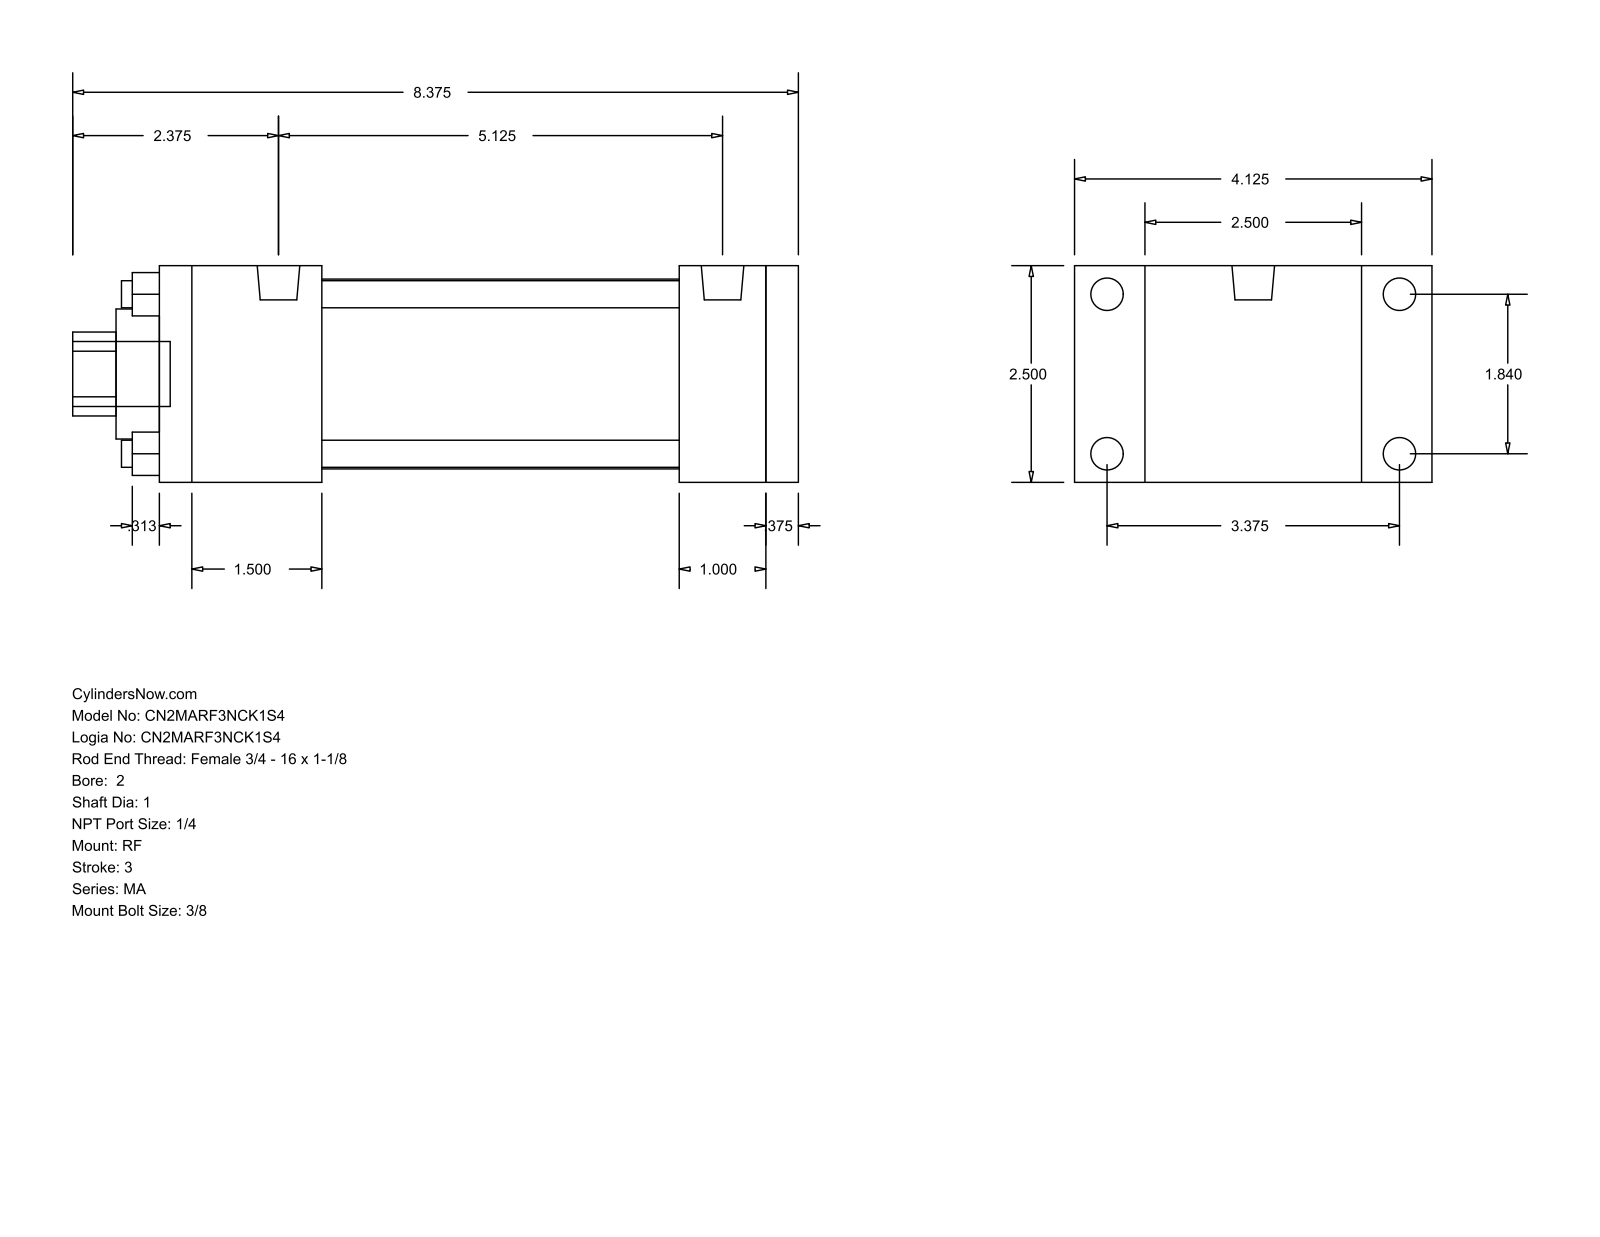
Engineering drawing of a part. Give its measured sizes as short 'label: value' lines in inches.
name: MA_RF__0200_1
written by: GSSL Pune (CONFIG_CONTROL_DESIGN)
unit: in
bodies: 0 solids, 92 faces (64 planar, 28 cylindrical, 0 other)
size: 8.375 × 4.125 × 2.5
holes: 4× ⌀0.313, 1× ⌀1, 1× ⌀1.5, 1× ⌀2.19
bosses: 4× ⌀0.375, 4× ⌀0.313, 2× ⌀0.492, 1× ⌀0.75
rounds: 1× R0.484
face distances: 2.5, 7, 0.375, 7.375, 1, 0.813, 0.5, 1.875, 5.125, 5.5
hole spacings: 1.301, 1.84, 2.602
